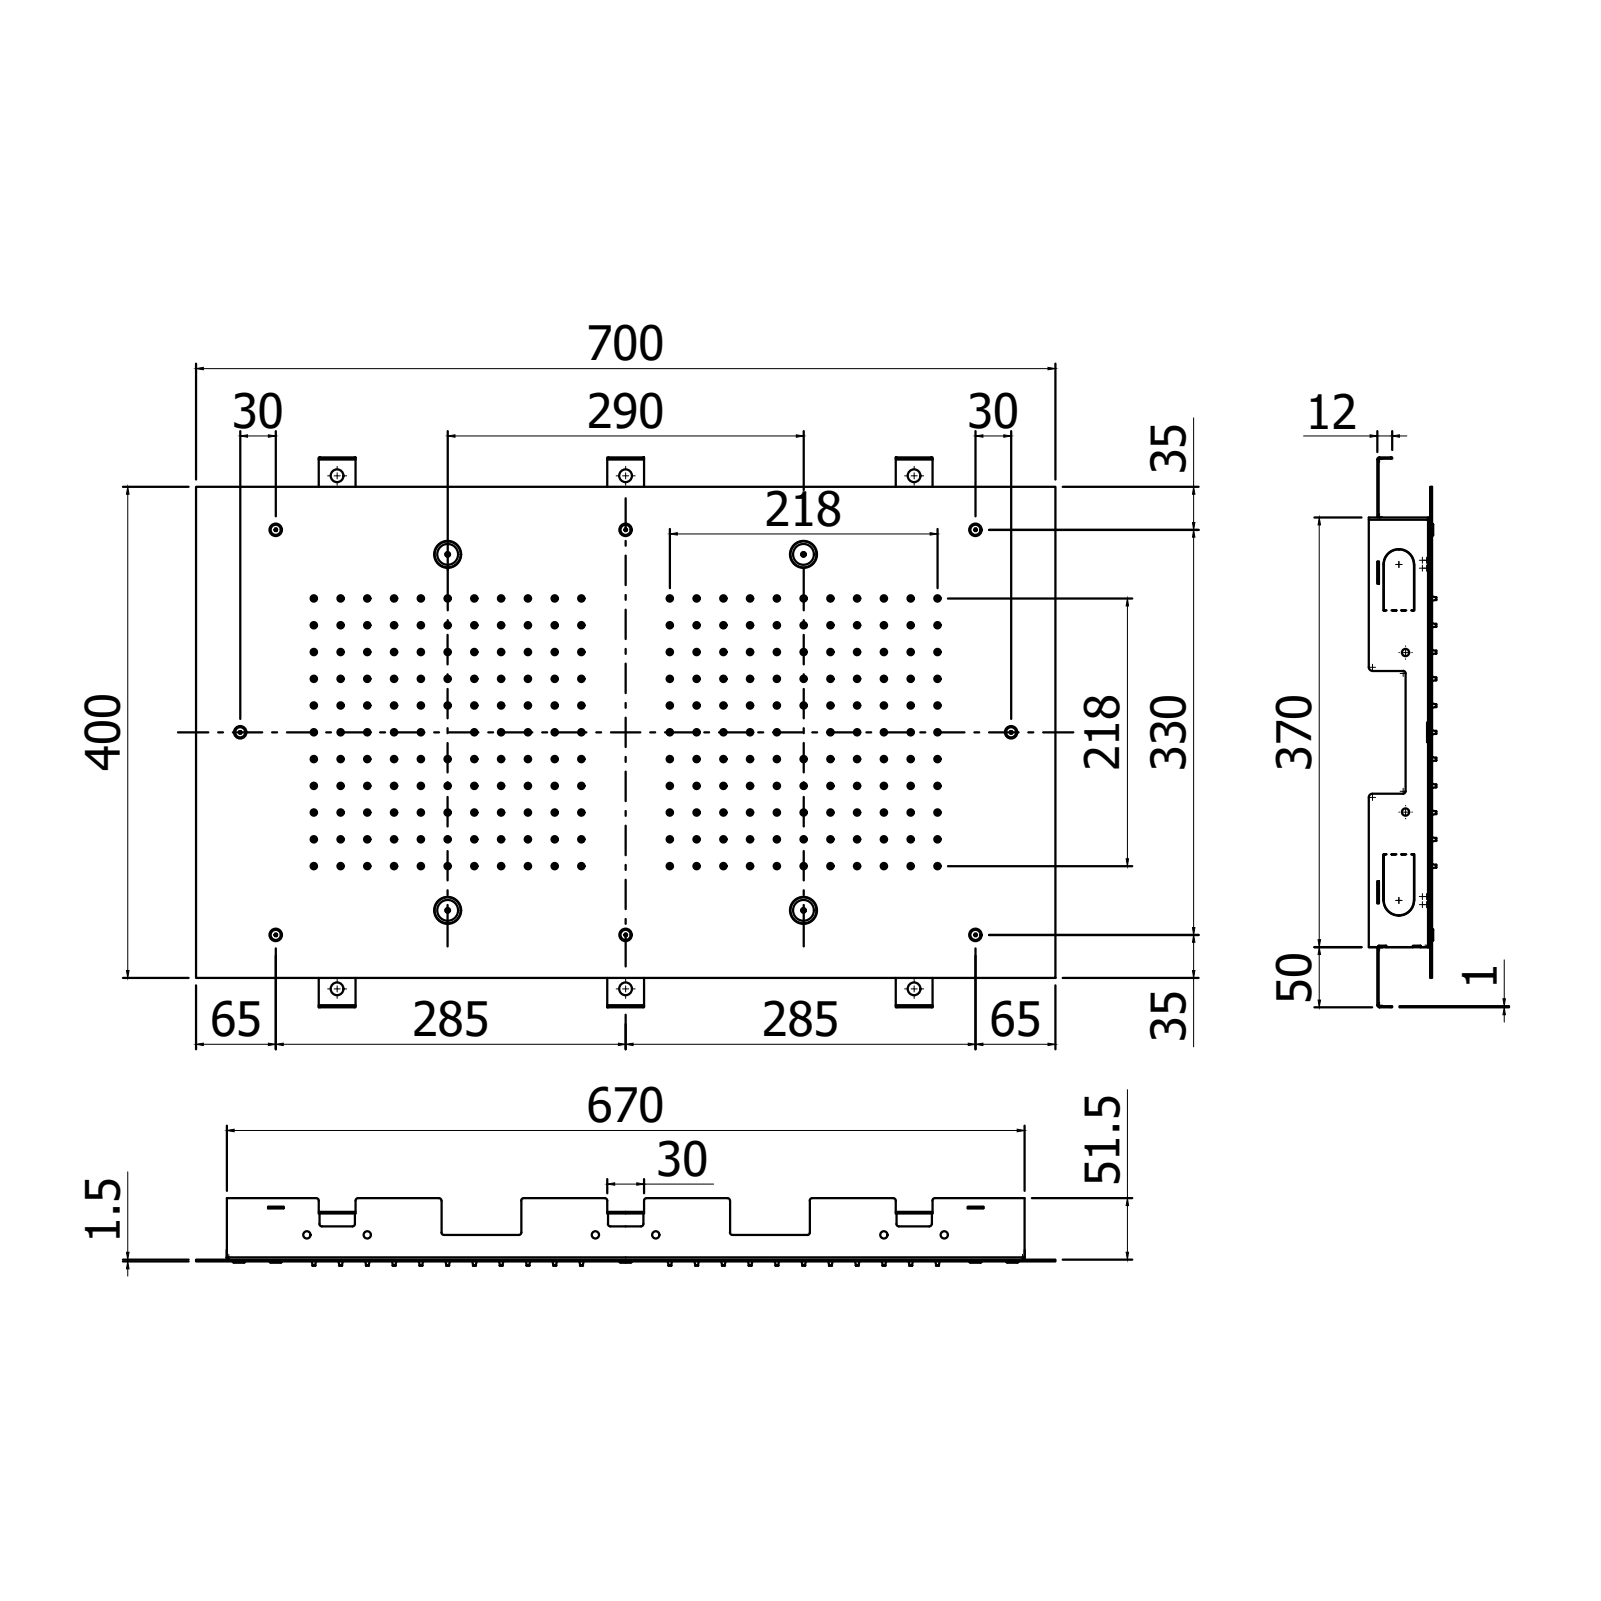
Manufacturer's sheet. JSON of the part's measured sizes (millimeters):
{"part_name": "ZSOF131CR", "step_written_by": "CREO PARAMETRIC BY PTC INC, 2020044 (CONFIG_CONTROL_DESIGN)", "units": "millimeters", "bodies": {"solids": 241, "faces": 4150, "planar": 562, "cylindrical": 1092, "other": 2496}, "overall_size": [700, 400, 4.8], "volume_mm3": 422519, "surface_area_mm2": 583510, "round_holes": [[1.5, 244], [5, 240], [7, 8], [17.05, 4]], "round_bosses_or_shafts": [[10, 8], [5, 8], [20, 4], [16.65, 4]], "partial_cylinders_radius": [[0.2, 48], [2, 4]], "face_to_face_distances": [1.5, 400, 700, 2.5, 1, 4.8, 3.3, 2.3, 2, 308], "hole_center_spacings": [68.94, 48.75, 111.16, 97.49, 78.6, 89.88, 109, 30.83]}
